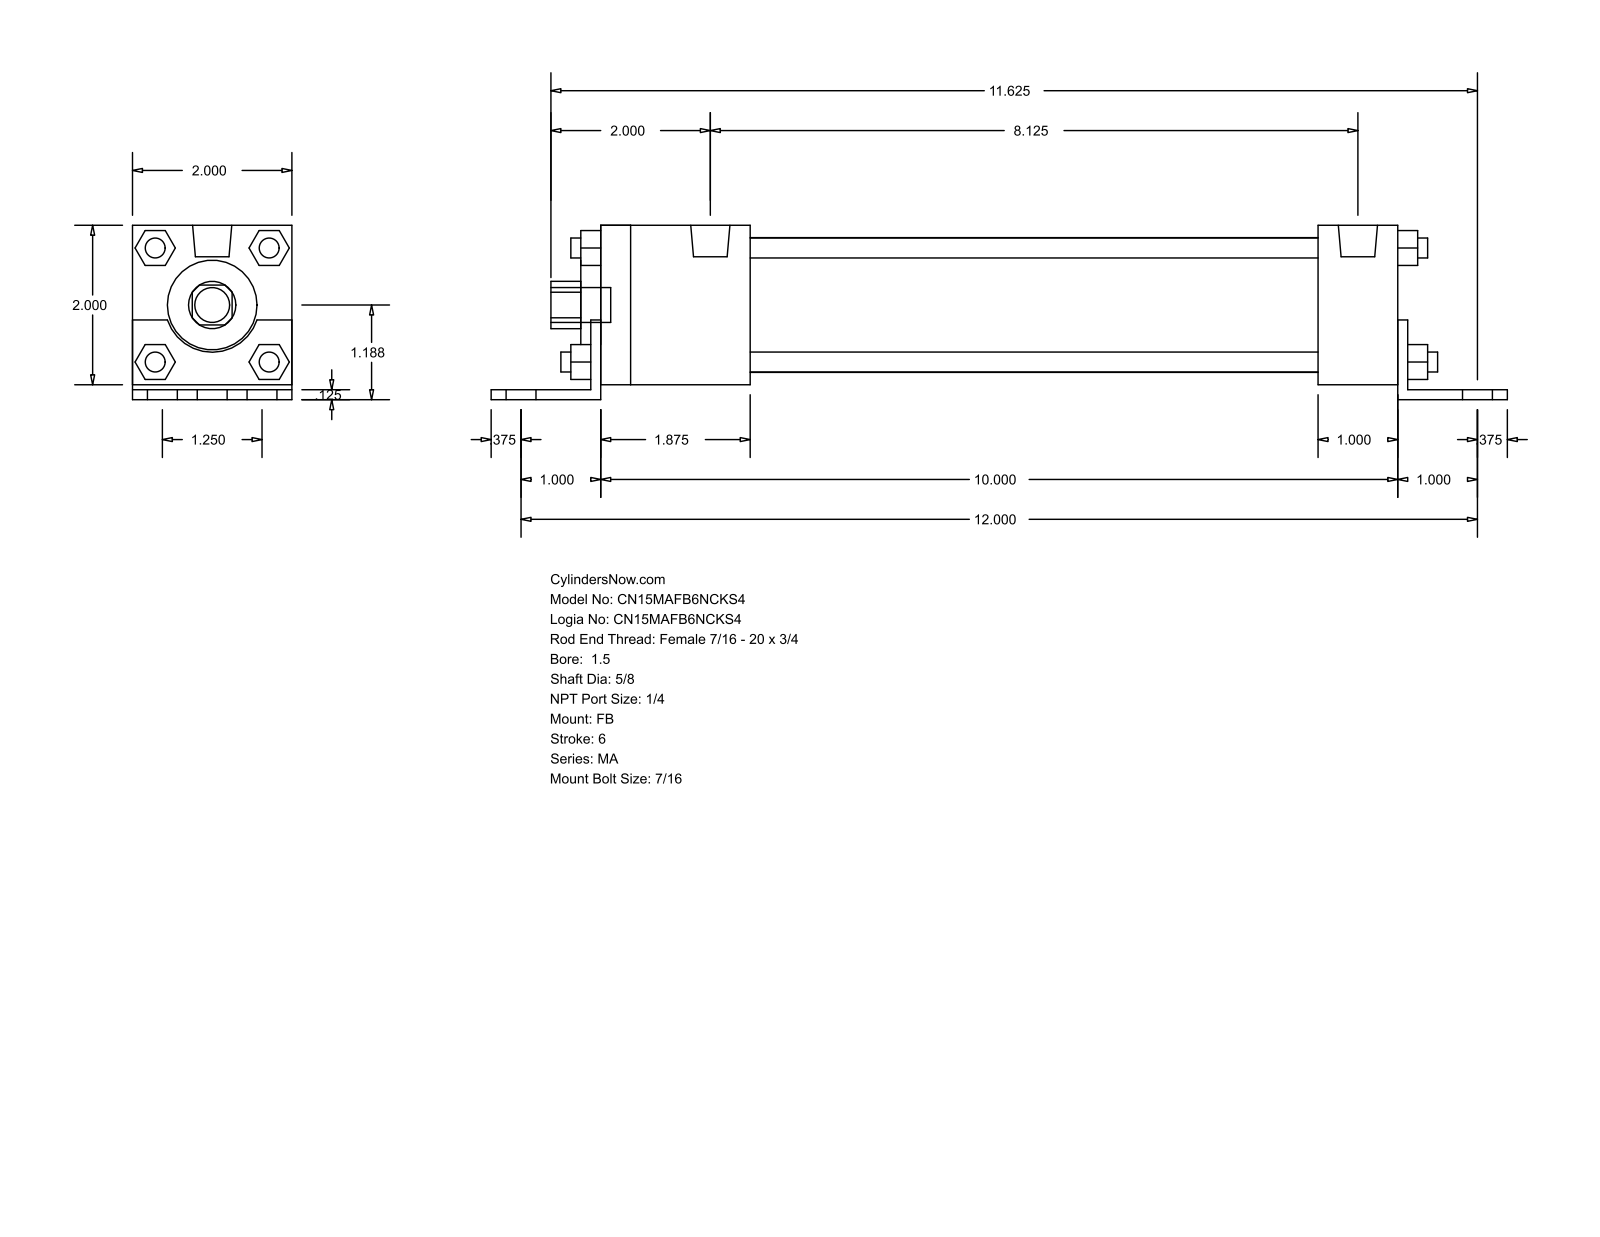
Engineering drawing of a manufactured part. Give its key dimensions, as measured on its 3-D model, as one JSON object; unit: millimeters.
{"part_name": "MA_FB__0150_0.625", "step_written_by": "GSSL Pune (CONFIG_CONTROL_DESIGN)", "units": "millimeters", "bodies": {"solids": 0, "faces": 140, "planar": 105, "cylindrical": 35, "other": 0}, "overall_size": [323.85, 55.56, 50.8], "round_holes": [[15.88, 1], [28.57, 1], [42.93, 1]], "round_bosses_or_shafts": [[11.11, 7], [7.94, 4], [6.35, 4], [12.49, 2]], "partial_cylinders_radius": [[7.54, 1], [15.05, 1]], "face_to_face_distances": [50.8, 3.17, 4.76, 55.56, 1.59, 52.39, 260.35, 6.35, 254, 3.18]}
